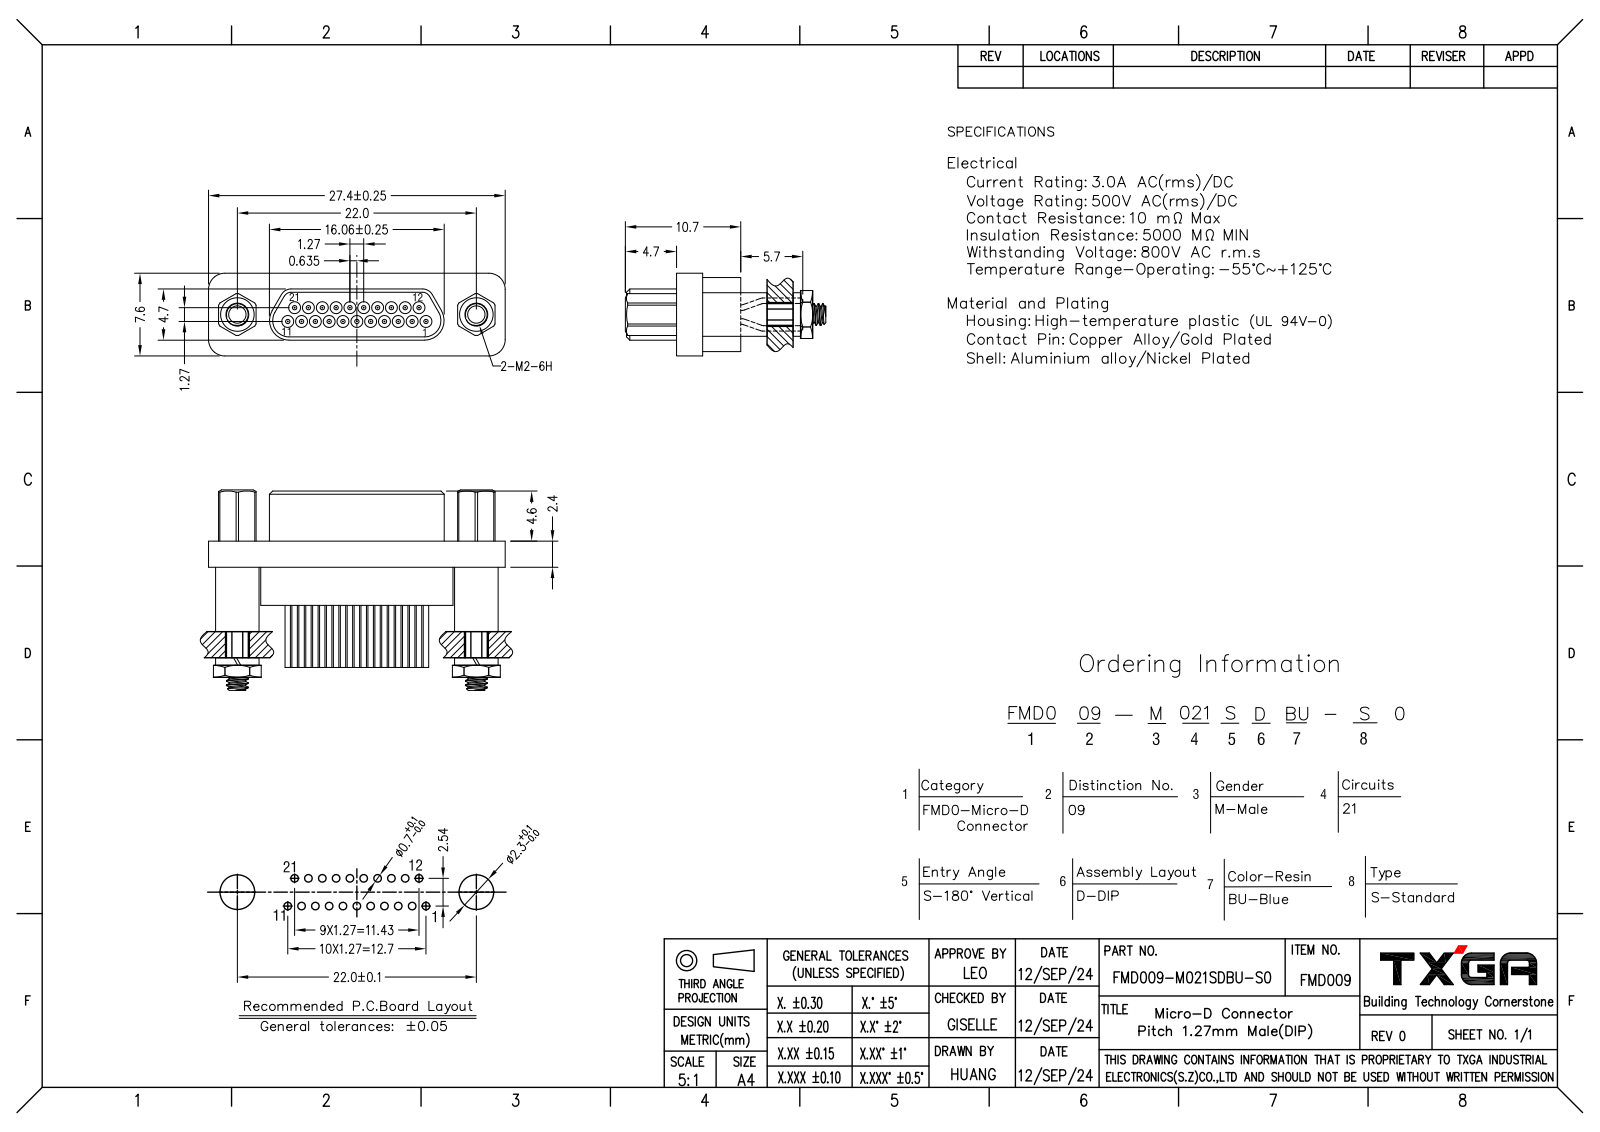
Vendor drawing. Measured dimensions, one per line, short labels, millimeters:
name: FMD009-M021SDBU-S0
written by: SolidWorks 2021 (CONFIG_CONTROL_DESIGN)
unit: mm
bodies: 1 solid, 1575 faces (625 planar, 448 cylindrical, 502 other)
size: 27.4 × 18.6 × 7.6
volume: 1 444 mm³; area: 2 310 mm²
holes: 21× ⌀1.1, 2× ⌀1.6, 2× ⌀2.1, 2× ⌀2.2, 2× ⌀2.3
bosses: 63× ⌀0.5, 21× ⌀0.45, 2× ⌀4.3, 2× ⌀4, 2× ⌀3.5, 2× ⌀3.1, 2× ⌀2
rounds: 12× R0.3, 10× R1.5, 4× R1.8, 2× R1.3
face distances: 5.9, 1.45, 6.15, 0.4, 7.2, 1.05, 5.75, 2.4, 3.5, 7.6
hole spacings: 1.27, 2.2, 3.36, 2.54, 3.81, 5.08, 4.58, 5.82
